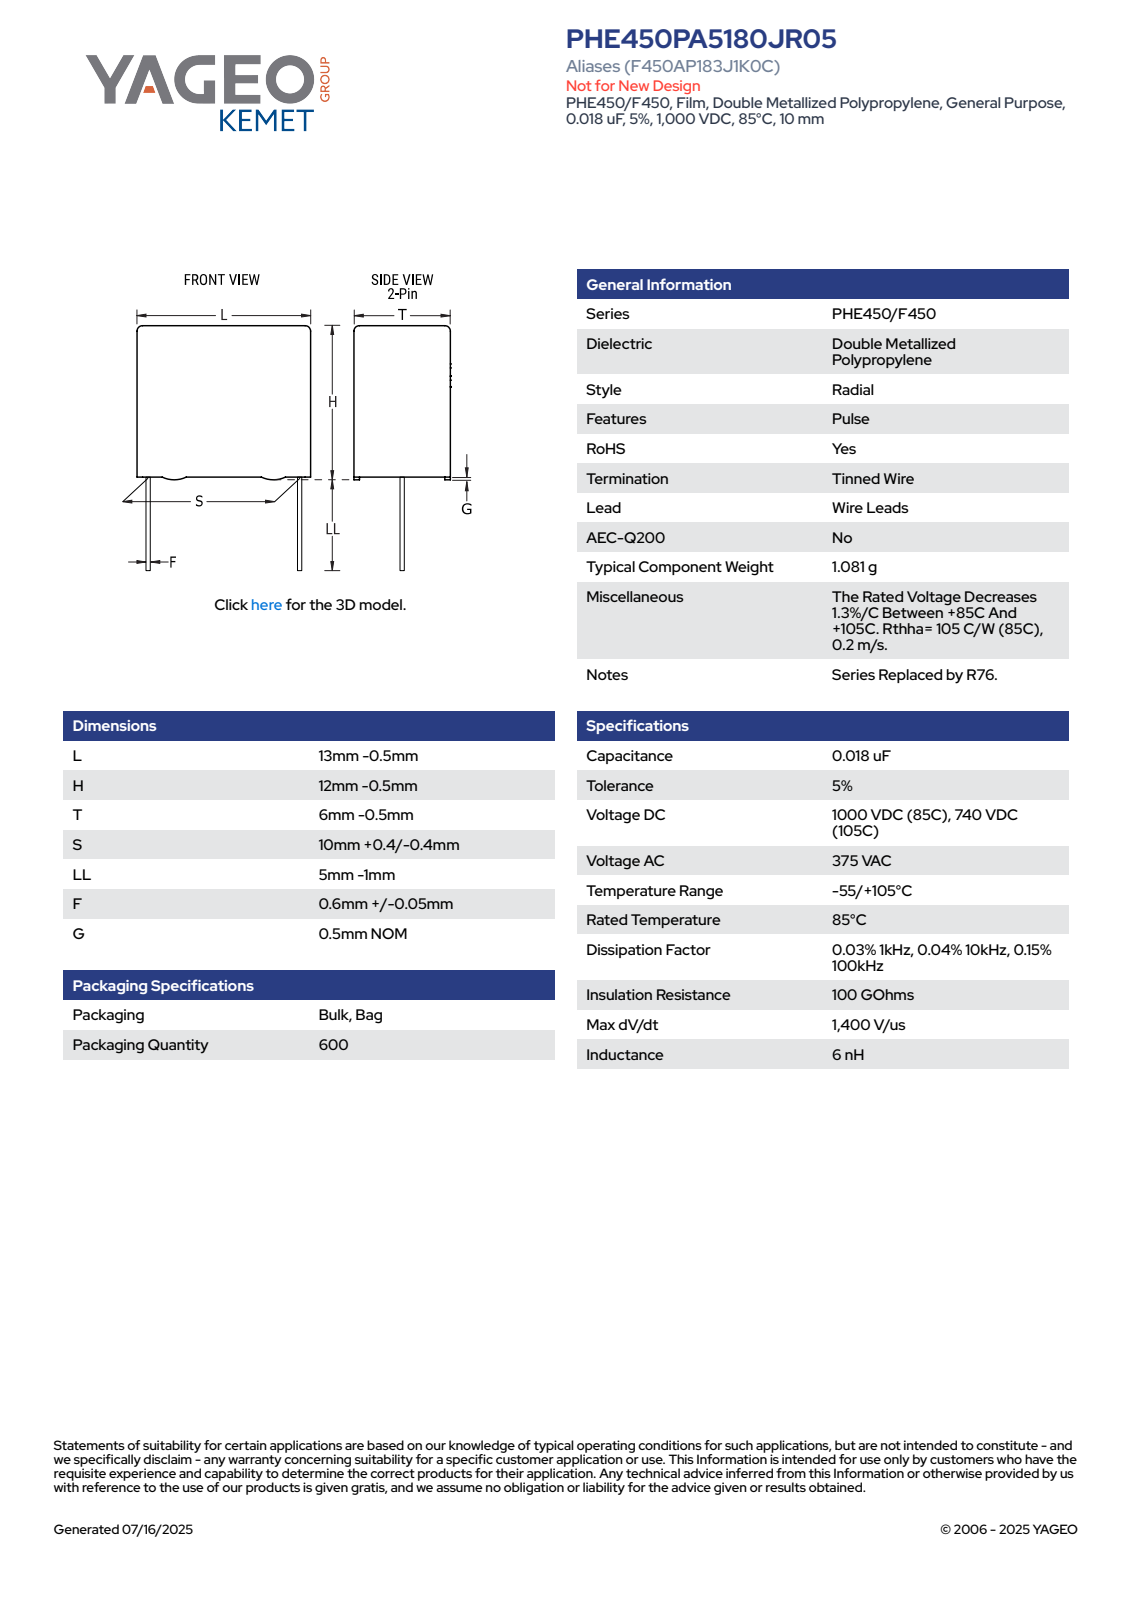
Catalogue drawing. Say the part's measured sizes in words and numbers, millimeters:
The part is named "CFR_RBG_13X12X6_L12.5H11.5T5.5S10LL4F0.65G0.5". Its 3-D file was written by "SolidWorks 2020 (AUTOMOTIVE_DESIGN)". It is 4 solids with 89 faces: 81 planar, 8 cylindrical and 0 other. Overall it measures 15.5 by 12.5 by 5.5 millimeters. Its volume is 759 cubic millimeters and its surface area 570 square millimeters. Round bosses or shafts: 2 of diameter 0.65. Partial cylindrical surfaces (rounded edges, fillets, slot ends): 4 of radius 0.5. The main face-to-face distances are 5.5, 12.5, 11, 0.31, 5.19, 0.5, 11.5, 4.88, 4, 4.5.
